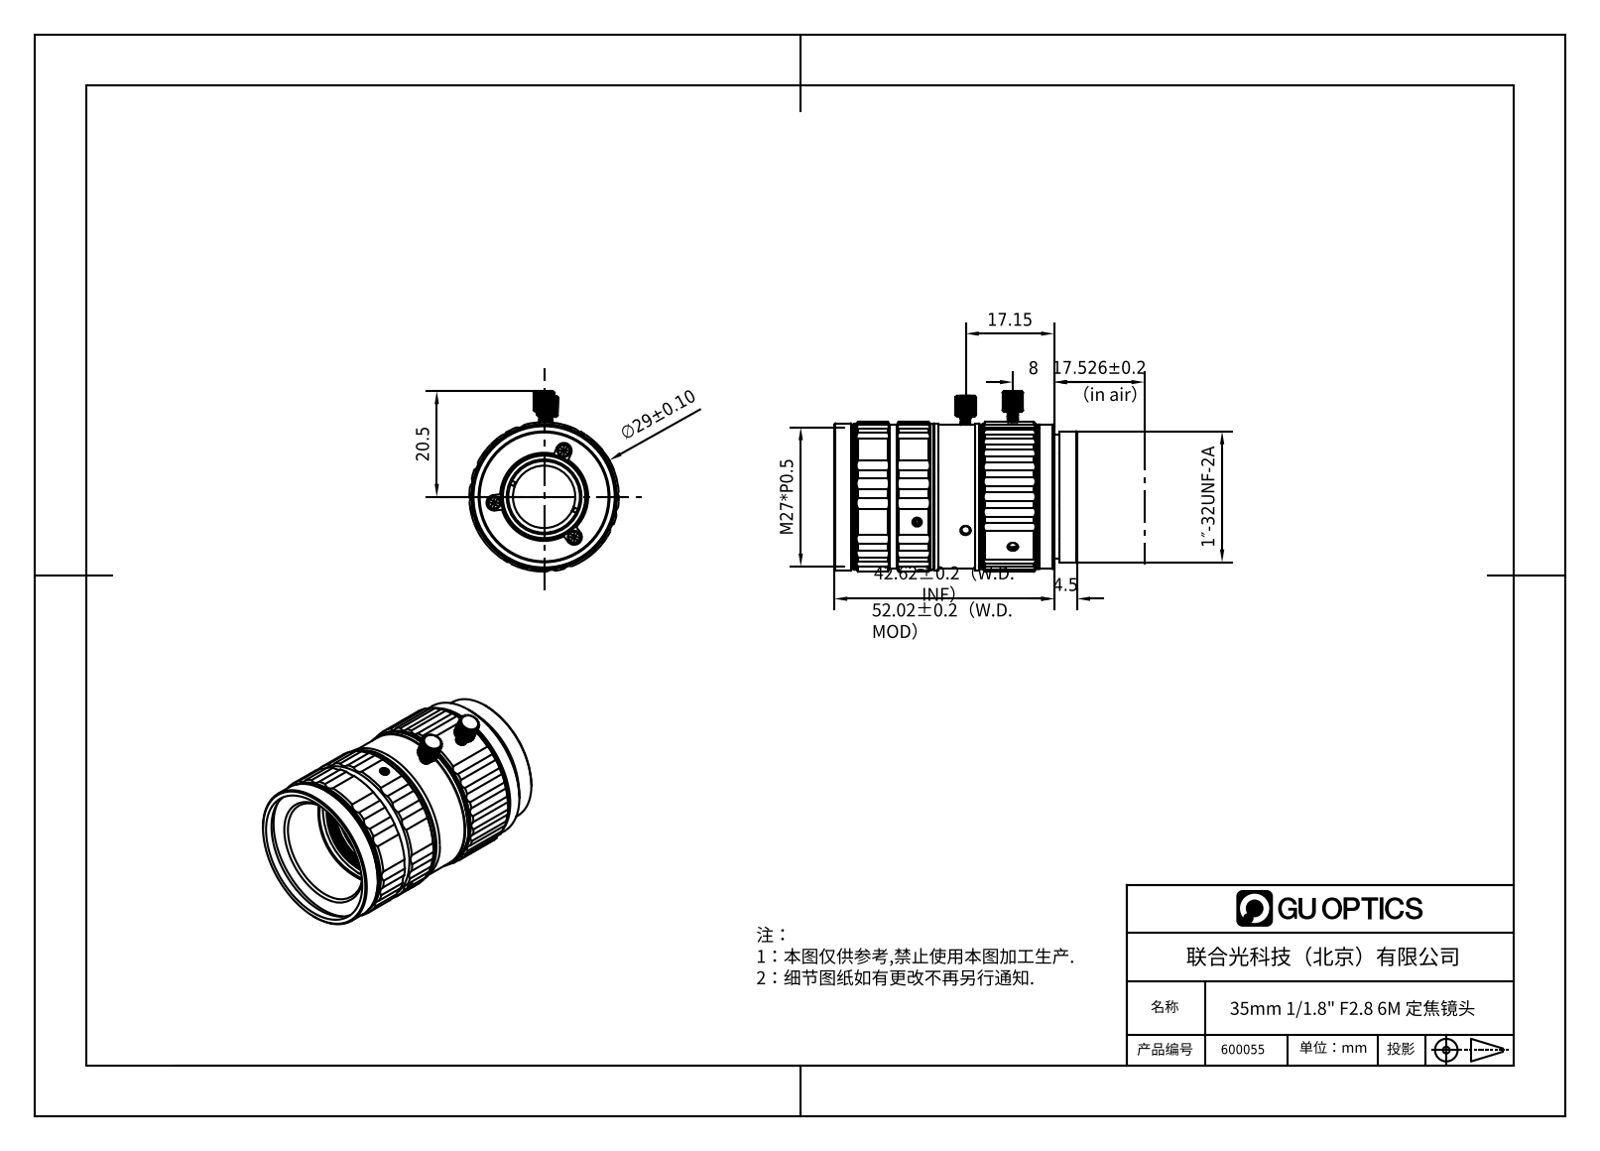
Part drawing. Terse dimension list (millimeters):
name: 600055
written by: SolidWorks 2020 (CONFIG_CONTROL_DESIGN)
unit: mm
bodies: 12 solids, 1391 faces (296 planar, 755 cylindrical, 340 other)
size: 47.12 × 34.01 × 28.98
volume: 23 337 mm³; area: 12 004 mm²
holes: 8× ⌀1.6, 4× ⌀2, 3× ⌀1.2, 3× ⌀1.22, 3× ⌀1.65, 3× ⌀1.7, 1× ⌀1.62, 1× ⌀12.1, 1× ⌀13.9, 1× ⌀14.7, 1× ⌀14.9, 1× ⌀15.5
bosses: 6× ⌀1.6, 3× ⌀2.5, 3× ⌀1.2, 3× ⌀1.2, 2× ⌀2, 1× ⌀29, 1× ⌀28.5, 1× ⌀28.4
rounds: 26× R1.5, 18× R2.3, 6× R3.39, 5× R1.11, 4× R3.43, 3× R1, 2× R0.3, 2× R0.8
face distances: 1, 43.62, 44.62, 40.12, 10.69, 43.43, 1.19, 4.5, 38.93, 39.12
hole spacings: 9.75, 16.88, 16.89, 9.74
